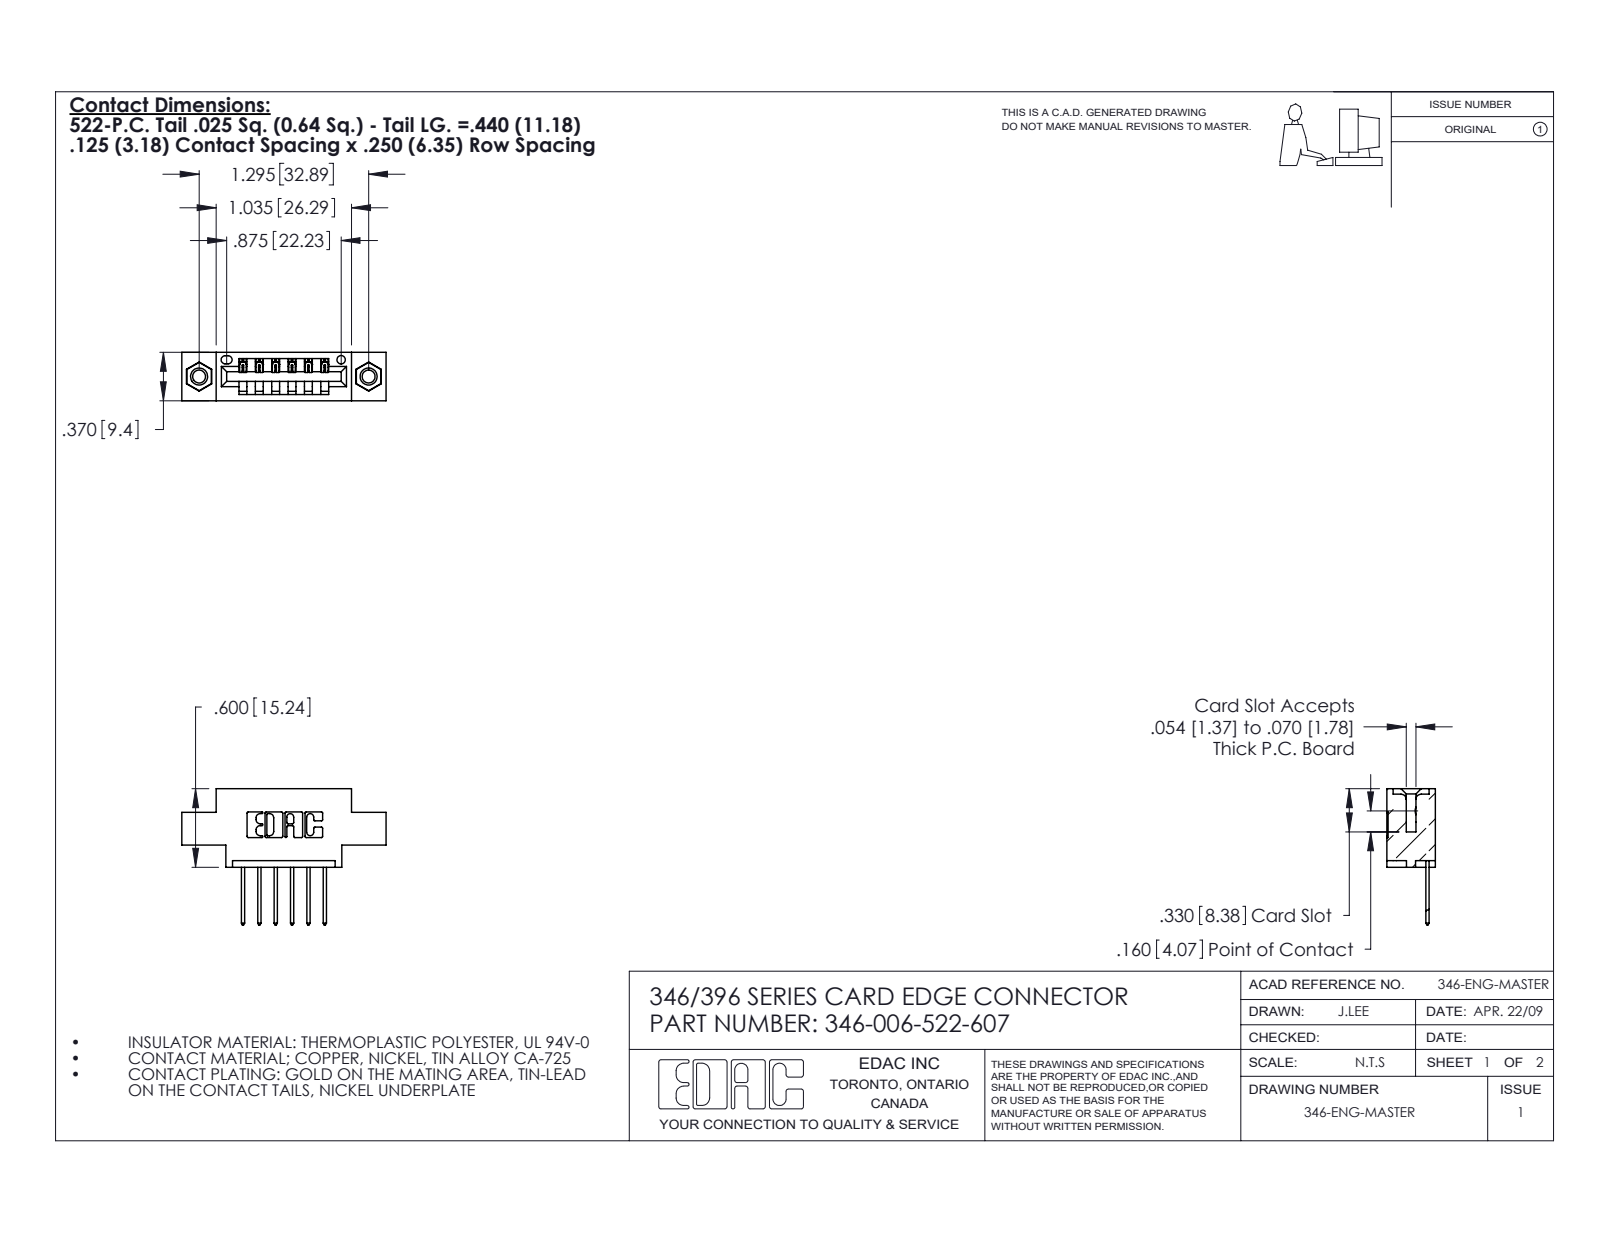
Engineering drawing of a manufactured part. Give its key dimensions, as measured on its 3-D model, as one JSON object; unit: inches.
{"part_name": "345-250-001_345-250-005-103; 346-006-522-607; 345-292-001_345-293-122; 346 Part_0.170 Offset - 0.156 Dia-TI", "step_written_by": "SolidWorks 2020 (CONFIG_CONTROL_DESIGN)", "units": "inches", "bodies": {"solids": 9, "faces": 534, "planar": 352, "cylindrical": 166, "other": 16}, "overall_size": [1.56, 1.04, 0.37], "volume_in3": 0.206, "surface_area_in2": 6.278, "round_holes": [[0.098, 2], [0.125, 2], [0.156, 2], [0.064, 1]], "round_bosses_or_shafts": [[0.155, 2]], "partial_cylinders_radius": [[0.01, 22], [0.006, 12], [0.01, 12], [0.007, 6], [0.031, 6], [0.026, 3], [0.031, 2], [0.04, 2]], "face_to_face_distances": [0.25, 0.37, 0.048, 0.322, 0.222, 0.148, 0.072, 0.298, 0.025, 0.1], "hole_center_spacings": [0.246, 1.092, 1.295]}
